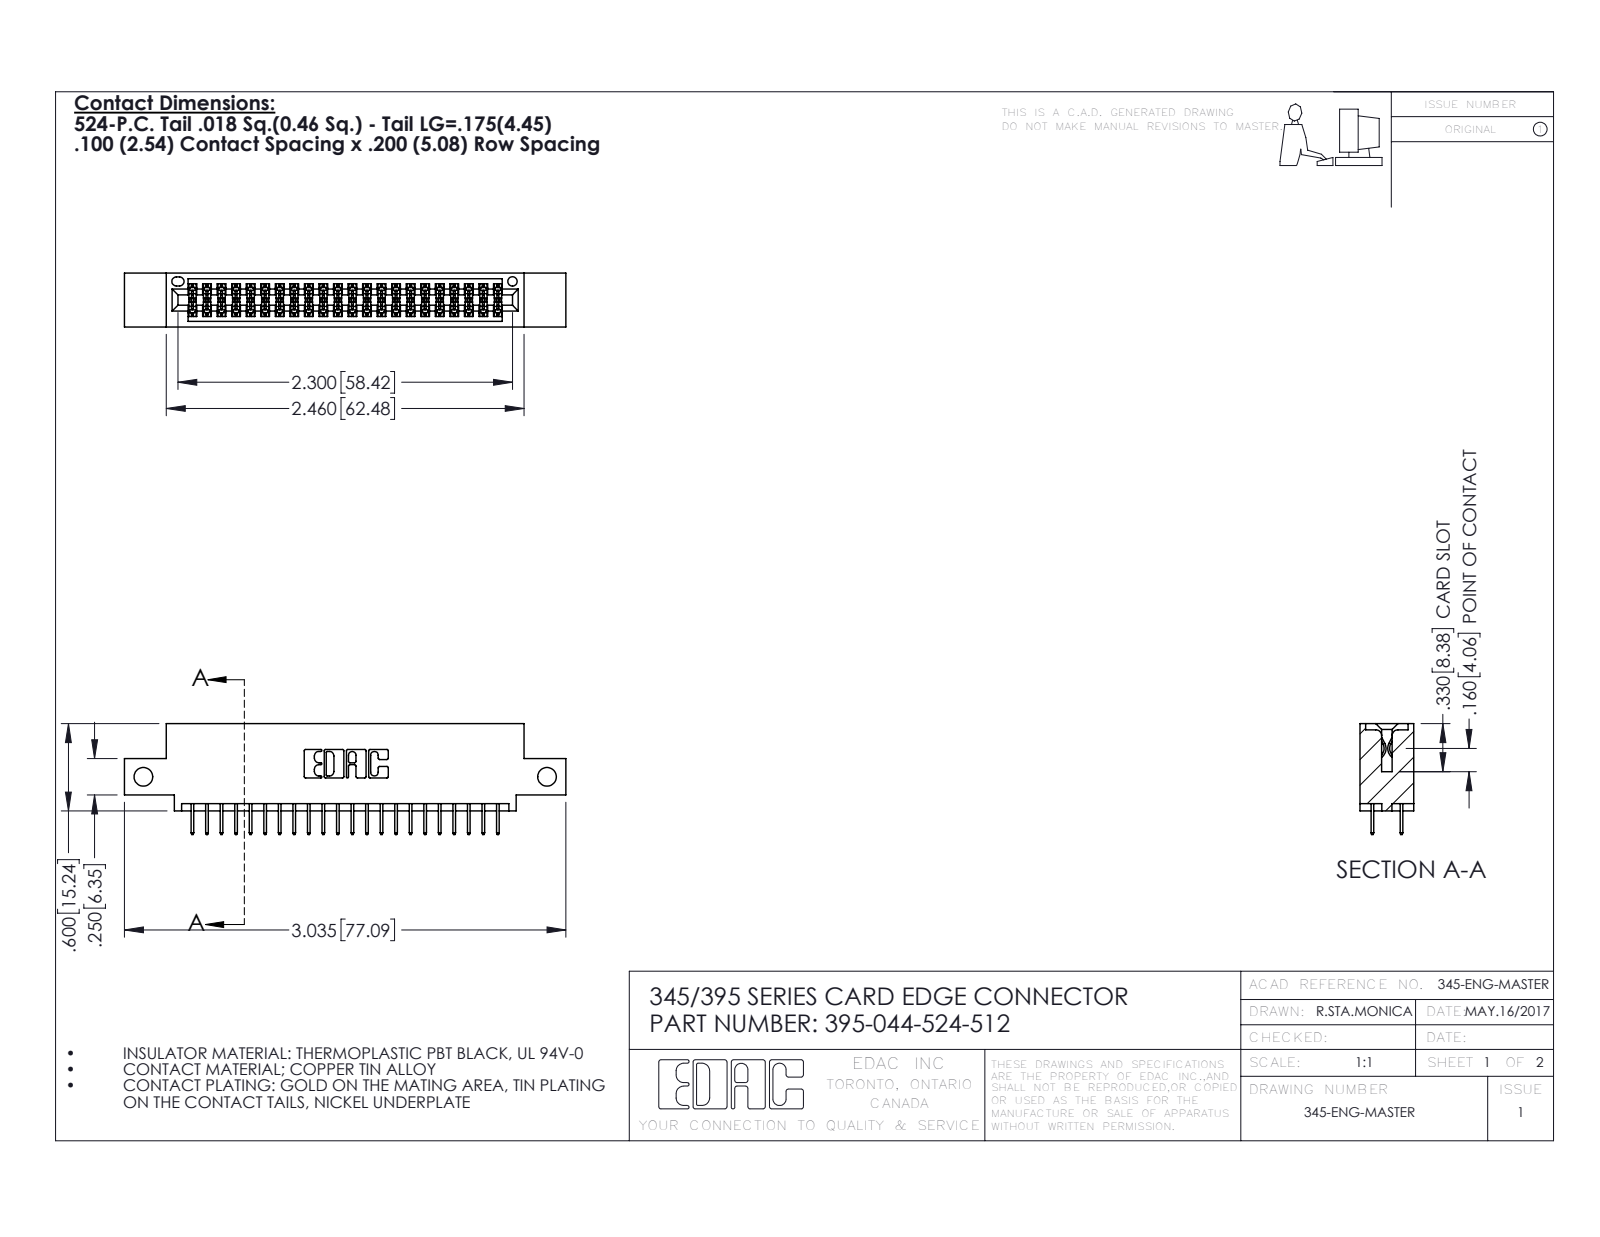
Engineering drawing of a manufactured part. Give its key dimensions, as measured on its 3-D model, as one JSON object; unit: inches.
{"part_name": "345 Part_0.110 Offset - Side Mount; 395-044-524-512; 345-292-001_345-293-124", "step_written_by": "SolidWorks 2016 (CONFIG_CONTROL_DESIGN)", "units": "inches", "bodies": {"solids": 45, "faces": 2506, "planar": 1800, "cylindrical": 706, "other": 0}, "overall_size": [3.035, 0.762, 0.37], "volume_in3": 0.432, "surface_area_in2": 15.27, "round_holes": [[0.128, 2], [0.064, 1]], "partial_cylinders_radius": [[0.006, 66], [0.01, 22], [0.007, 6], [0.031, 6], [0.026, 3], [0.014, 2], [0.019, 2], [0.022, 2]], "face_to_face_distances": [0.072, 0.298, 0.2, 0.37, 0.098, 0.272, 0.025, 0.225, 0.072, 0.175], "hole_center_spacings": [2.775]}
